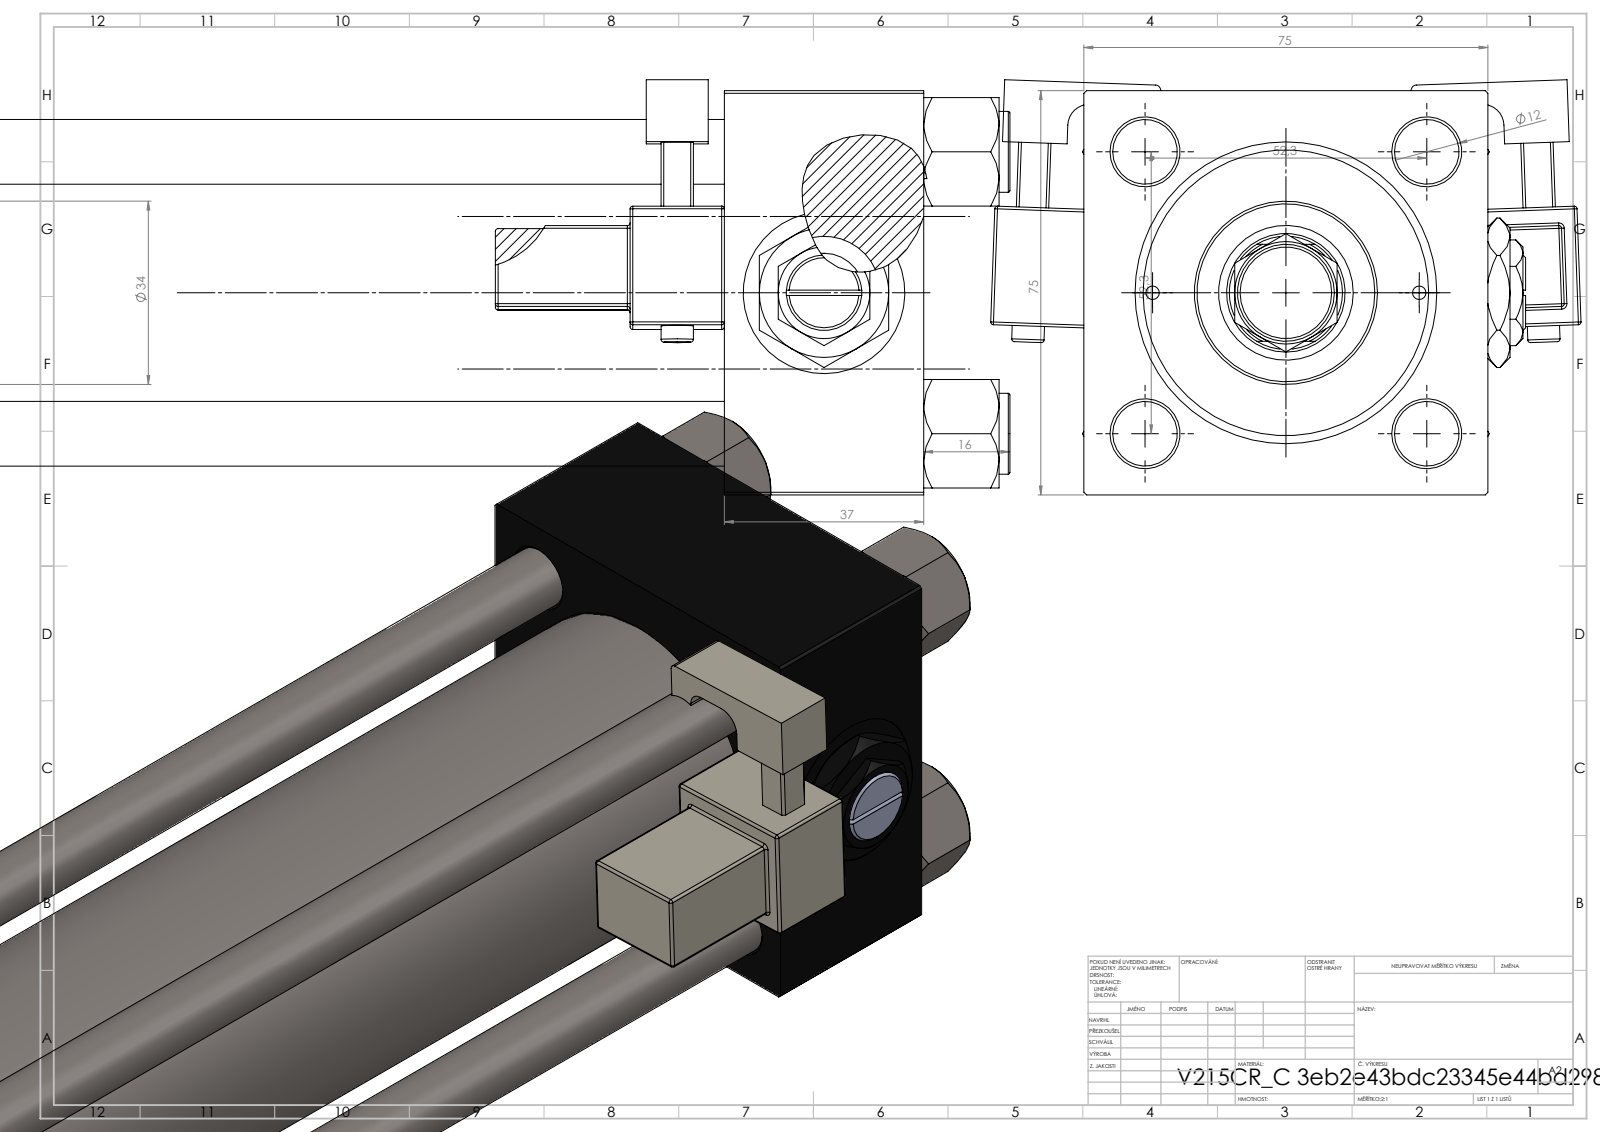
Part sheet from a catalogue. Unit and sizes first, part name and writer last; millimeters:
Units: millimetres
Overall size (bounding box): 558 × 109.57 × 77.03
Round holes (diameter × count): ⌀12 ×4, ⌀2.5 ×2, ⌀7 ×2, ⌀20.96 ×2, ⌀30 ×2, ⌀10.5 ×1, ⌀22 ×1, ⌀25 ×1, ⌀41 ×1, ⌀50 ×1, ⌀53 ×1
Round bosses / shafts (diameter × count): ⌀15 ×4, ⌀6 ×2, ⌀56 ×1, ⌀34 ×1, ⌀18 ×1, ⌀11 ×1
Partial cylindrical surfaces — rounded edges, fillets, slot ends (radius × count): R0.5 ×48, R1 ×2, R2.5 ×2, R4 ×2, R10.5 ×1
Main face-to-face distances: 75, 37, 484, 447, 425, 388, 59, 455.3, 418.3, 30.3
Hole centre spacings: 26.19, 36.98, 52.3, 57.22, 24.75, 73.96, 49.5, 423.5
Volume: 1 141 000 mm³ · Surface area: 349 271 mm²
Bodies: 16 solids, 1461 faces (649 planar, 166 cylindrical, 646 other)
Part name (STEP PRODUCT): V215CR_C_Body; V215CR_C_TYCINKA; V215CR_MSU; NUT_M5_C (+4 more)
STEP written by: SolidWorks 2019 (CONFIG_CONTROL_DESIGN)
